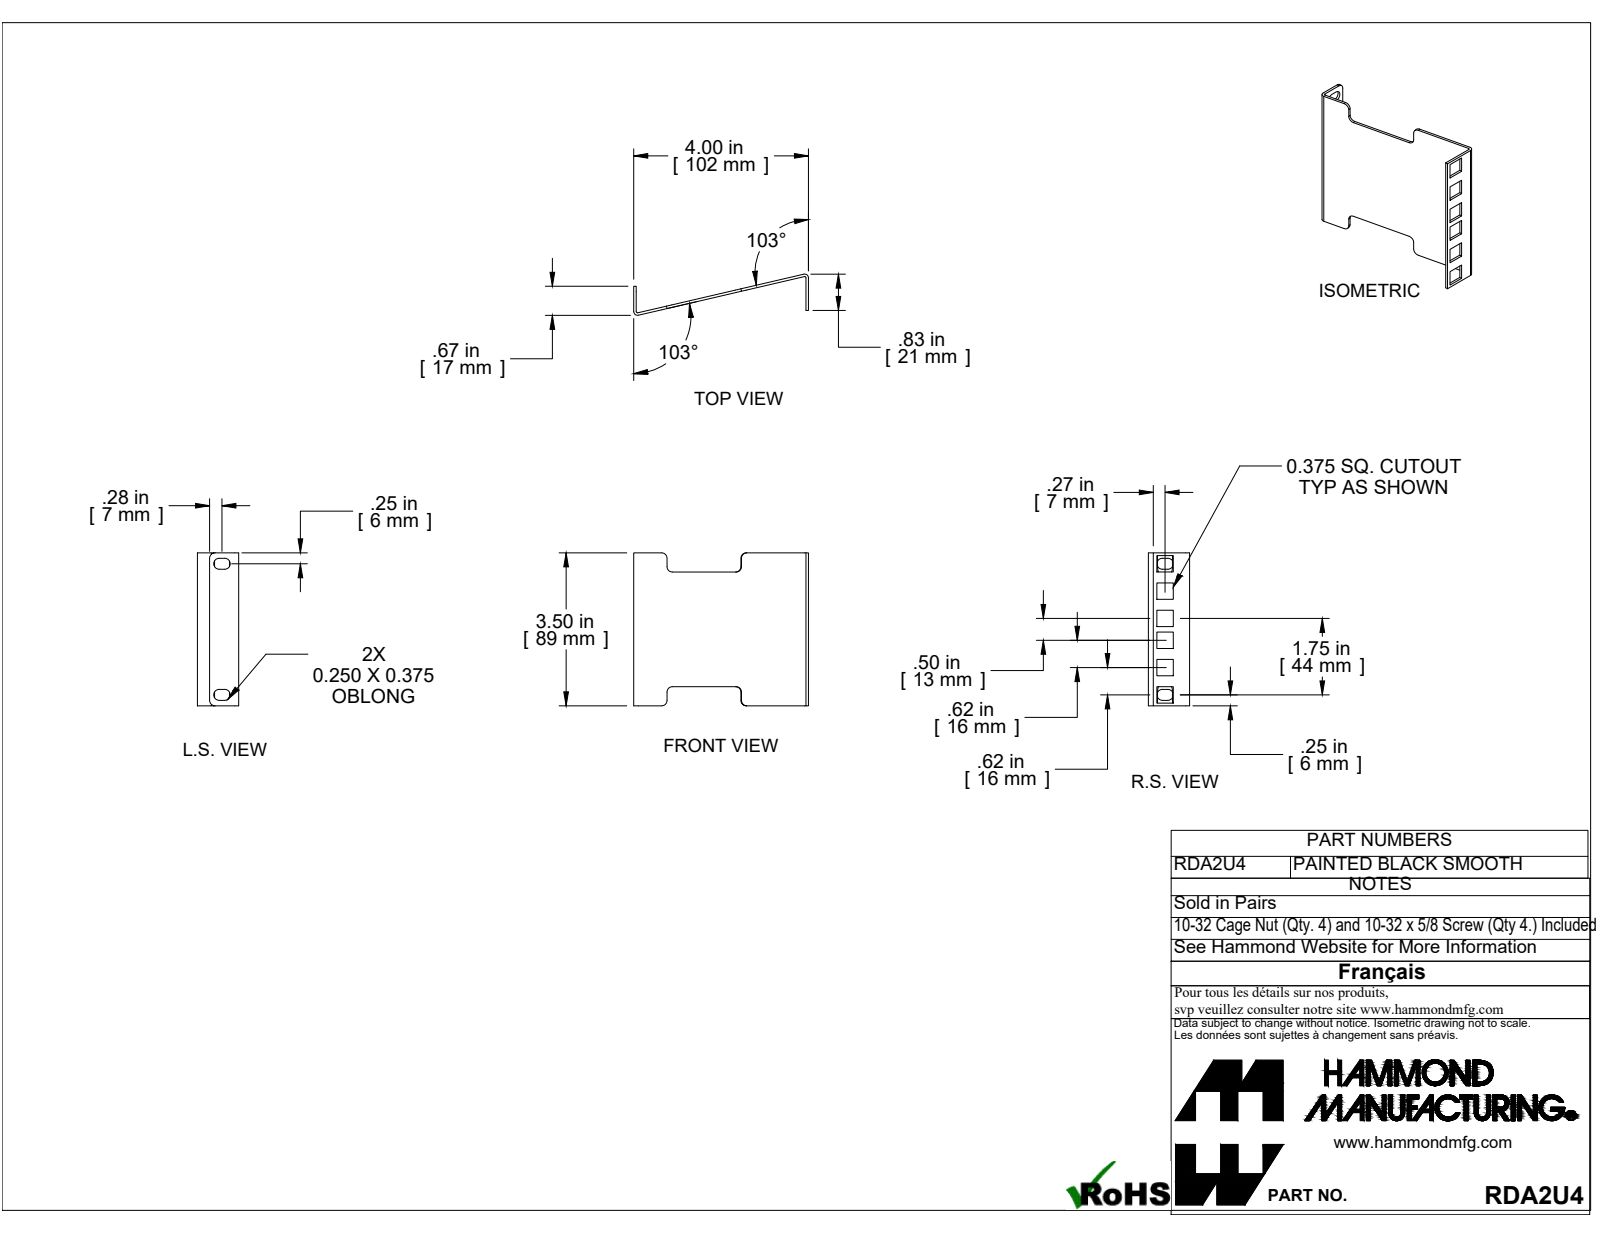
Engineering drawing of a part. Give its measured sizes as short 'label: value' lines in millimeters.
name: RDA2U4
written by: SolidWorks 2019 (CONFIG_CONTROL_DESIGN)
unit: mm
bodies: 1 solid, 64 faces (46 planar, 18 cylindrical, 0 other)
size: 101.6 × 88.9 × 24
volume: 15 400 mm³; area: 22 370 mm²
rounds: 14× R3.2, 2× R0.7, 2× R2.2
face distances: 1.4, 100.2, 98.7, 101.6, 88.9, 9.5, 14, 11.1, 77.8, 44.5
